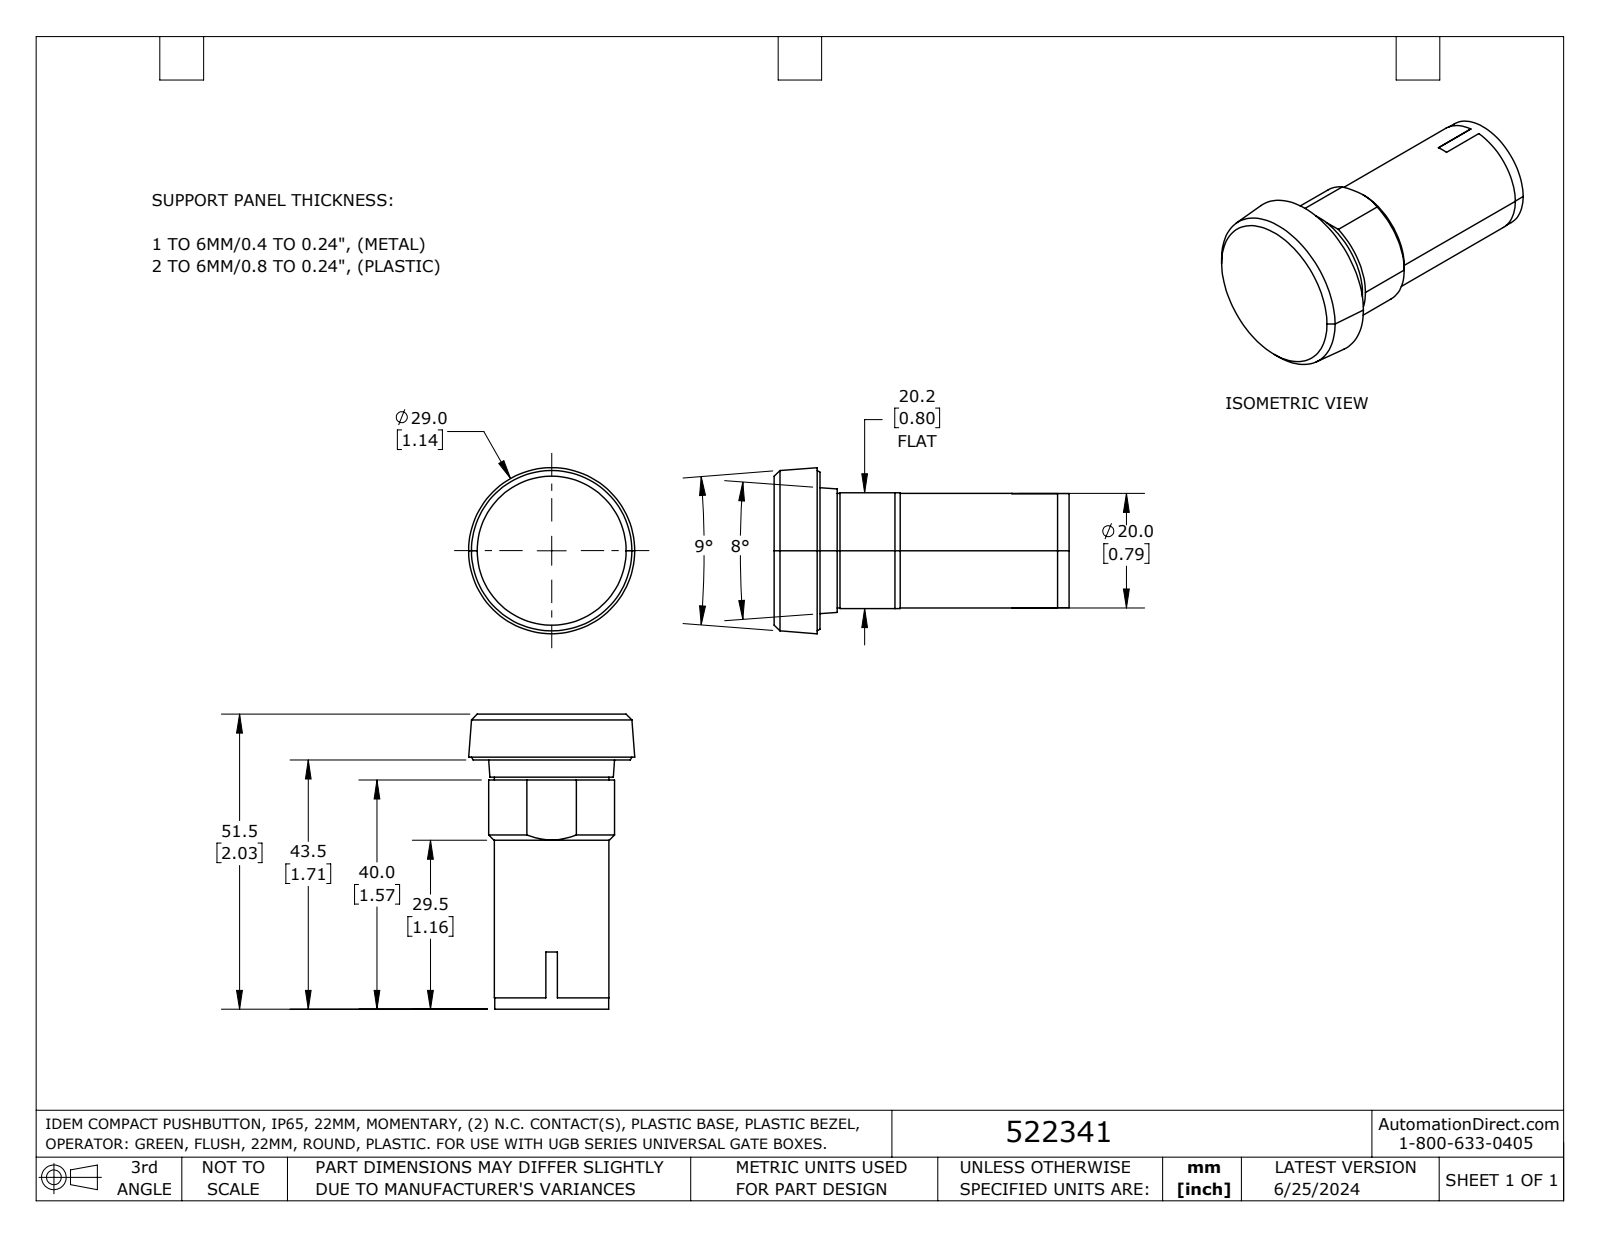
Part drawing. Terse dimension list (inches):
name: 522341
written by: SolidWorks 2023 (AUTOMOTIVE_DESIGN)
unit: in
bodies: 1 solid, 37 faces (17 planar, 10 cylindrical, 10 other)
size: 2.028 × 1.142 × 1.142
volume: 1.185 in³; area: 7.436 in²
bosses: 1× ⌀0.787, 1× ⌀0.783
rounds: 1× R0.433
face distances: 2.028, 0.315, 1.713, 0.138, 0.02, 0.797, 0.433, 0.453, 1.575, 0.118
